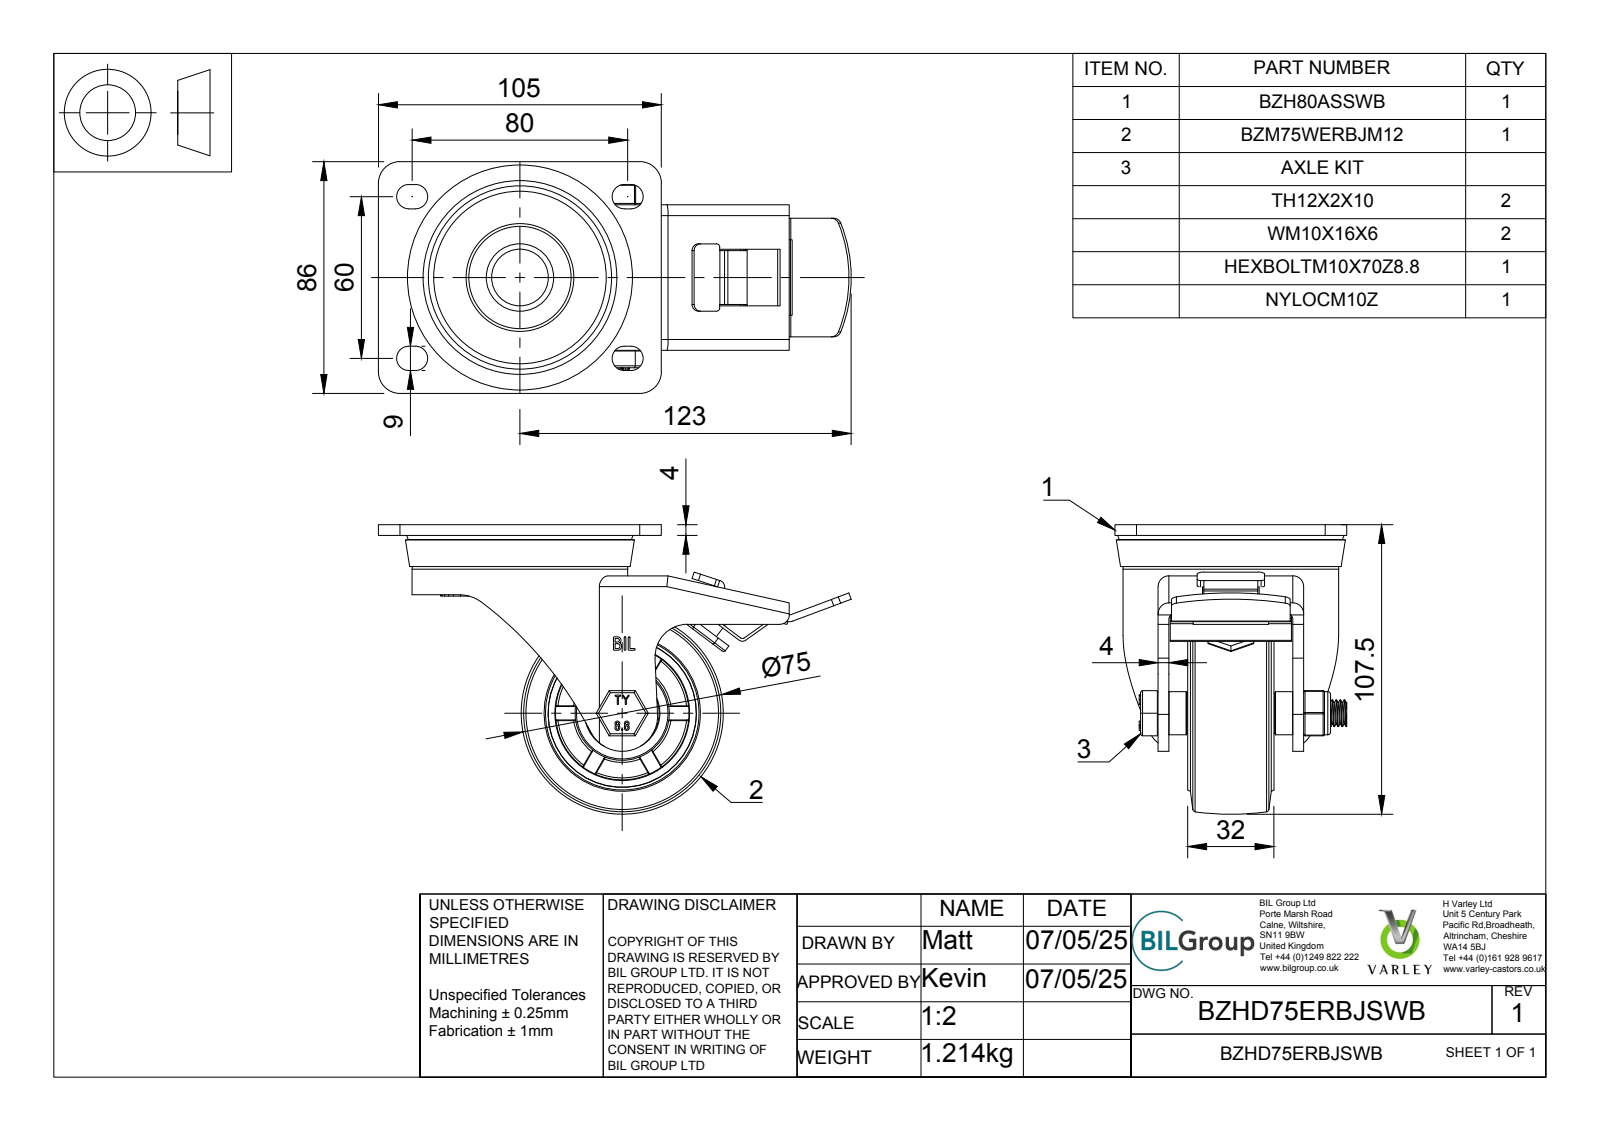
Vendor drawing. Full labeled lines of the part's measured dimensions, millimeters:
Part name (STEP PRODUCT): BZHD75ERBJSWB v4; BZH80ASSWB v1; ZINC PLATED, PRESSED STEEL TOP PLATE; ZINC PLATED, PRESSED STEEL FORKS (+8 more)
STEP written by: Autodesk Translation Framework v14.4.0.0 (AUTOMOTIVE_DESIGN)
Units: millimetres
Bodies: 42 solids, 1160 faces (422 planar, 328 cylindrical, 410 other)
Overall size (bounding box): 175.5 × 107.5 × 86
Volume: 246 239 mm³ · Surface area: 136 095 mm²
Round holes (diameter × count): ⌀8 ×1, ⌀10 ×1, ⌀10.2 ×1, ⌀10.4 ×1, ⌀12 ×1, ⌀17 ×1, ⌀17.5 ×1, ⌀17.75 ×1, ⌀24.72 ×1, ⌀25 ×1, ⌀25.5 ×1, ⌀26 ×1
Round bosses / shafts (diameter × count): ⌀80 ×1, ⌀59 ×1, ⌀35 ×1, ⌀31 ×1, ⌀20 ×1, ⌀18 ×1, ⌀16 ×1, ⌀15.5 ×1
Partial cylindrical surfaces — rounded edges, fillets, slot ends (radius × count): R0.25 ×23, R0.5 ×18, R0.75 ×12, R2 ×10, R4.5 ×8, R4 ×5, R2.5 ×4, R3 ×4
Main face-to-face distances: 4, 7.5, 1, 11.5, 7, 22, 3.5, 3, 15, 10.5
